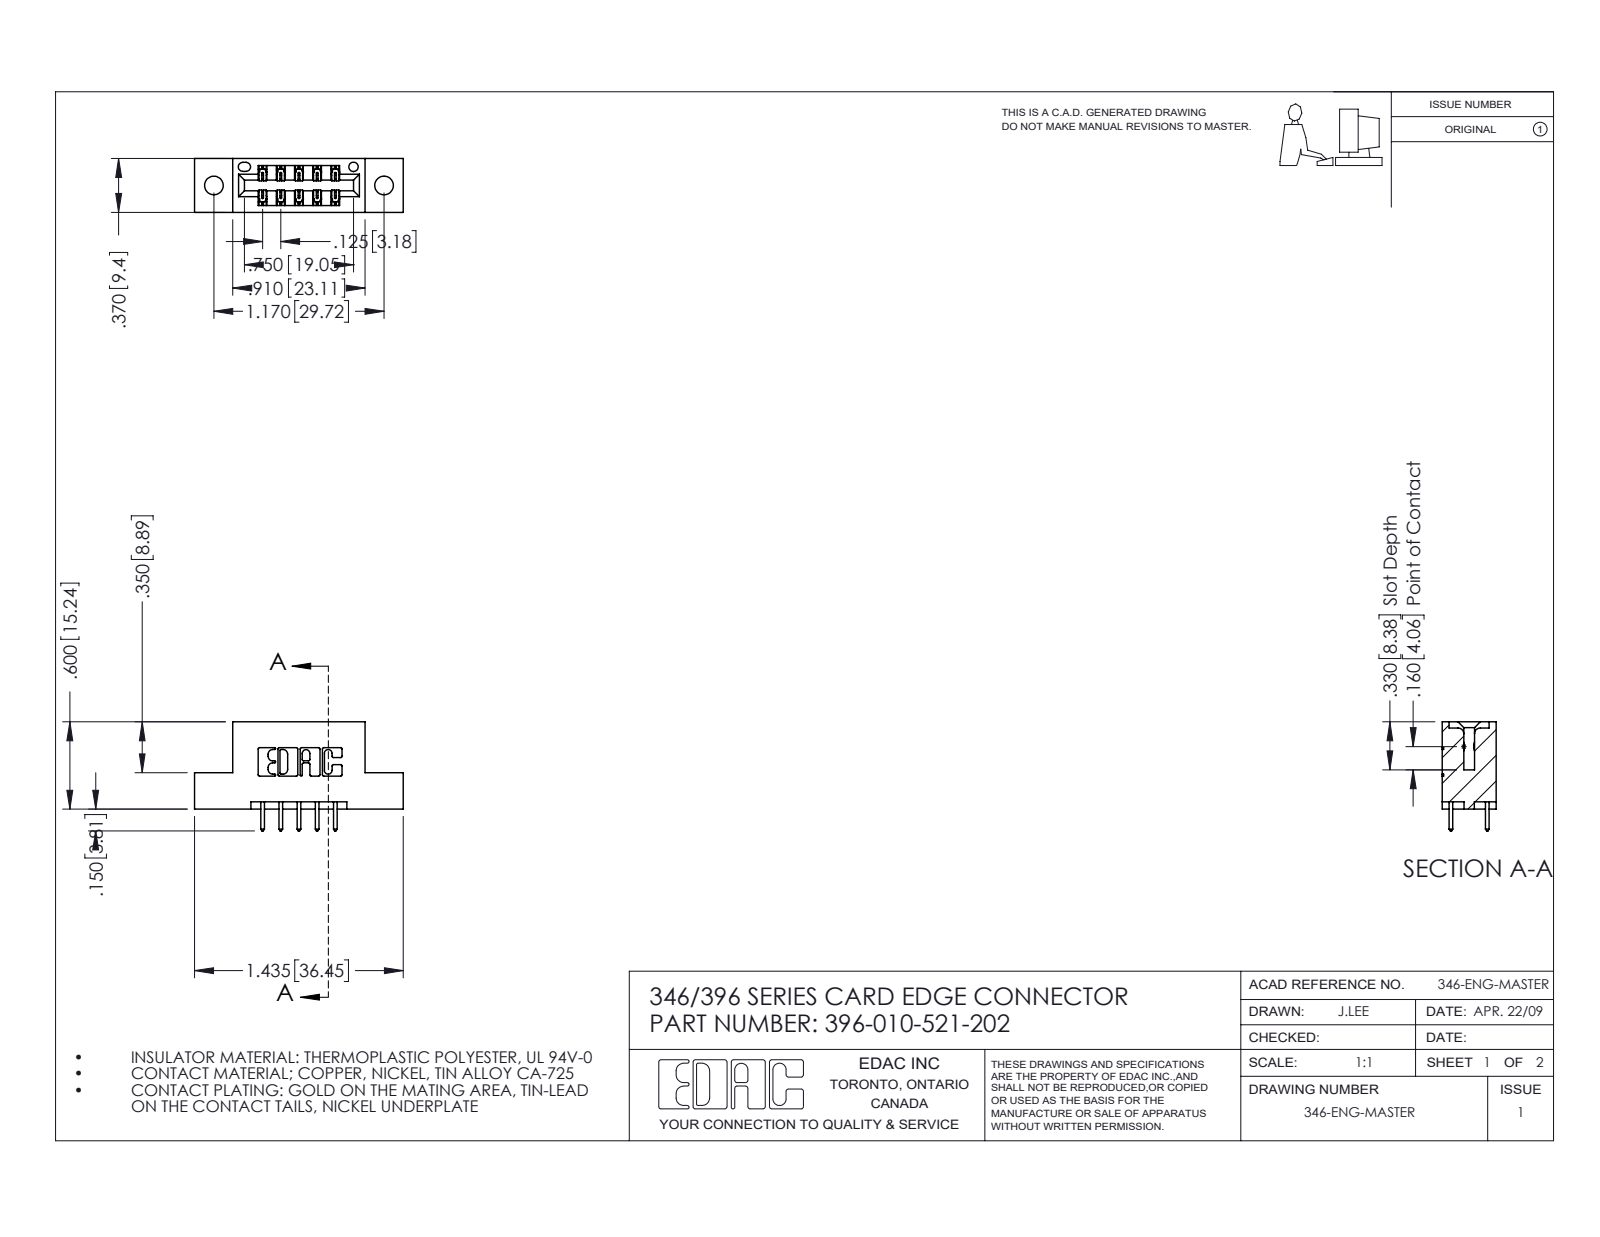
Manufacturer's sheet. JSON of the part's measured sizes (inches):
{"part_name": "345-292-001_345-293-121; 346 Part_Flush Mounting Lugs - 0.128 Dia; 396-010-521-202", "step_written_by": "SolidWorks 2016 (CONFIG_CONTROL_DESIGN)", "units": "inches", "bodies": {"solids": 11, "faces": 642, "planar": 426, "cylindrical": 216, "other": 0}, "overall_size": [1.435, 0.75, 0.37], "volume_in3": 0.197, "surface_area_in2": 5.512, "round_holes": [[0.128, 2], [0.064, 1]], "partial_cylinders_radius": [[0.01, 22], [0.006, 15], [0.01, 10], [0.007, 6], [0.031, 6], [0.026, 3], [0.014, 2], [0.022, 2]], "face_to_face_distances": [0.25, 0.37, 0.048, 0.322, 0.072, 0.298, 0.025, 0.148, 0.222, 0.1], "hole_center_spacings": [0.246, 0.969, 1.17]}
